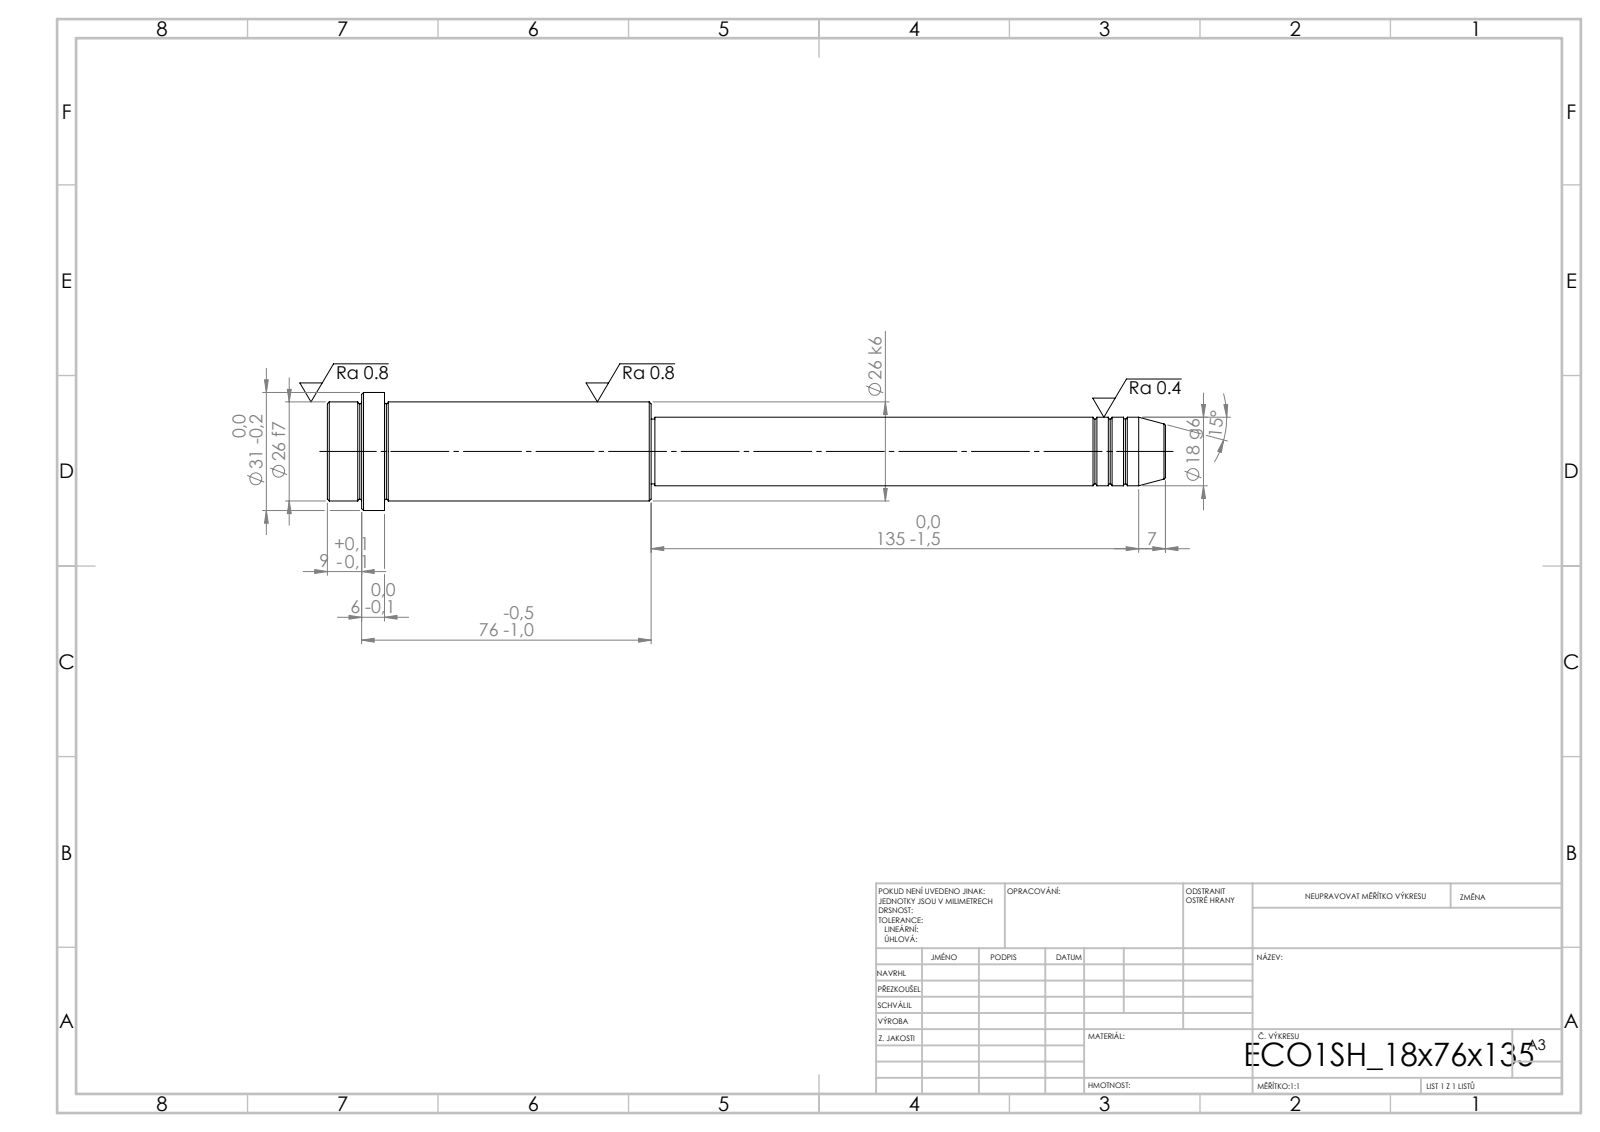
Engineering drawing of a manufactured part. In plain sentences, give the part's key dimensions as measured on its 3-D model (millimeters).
Its 3-D file was written by "SolidWorks 2019 (CONFIG_CONTROL_DESIGN)". It is 1 solid with 52 faces: 6 planar, 16 cylindrical and 30 other. Overall it measures 220 by 31 by 31 millimeters. Its volume is 80 291 cubic millimeters and its surface area 16 201 square millimeters. Round bosses or shafts: 1 of diameter 31, 1 of diameter 26, 1 of diameter 18, 1 of diameter 17. The main face-to-face distances are 85, 70, 15, 76, 6, 9, 135, 205, 211, 220.
